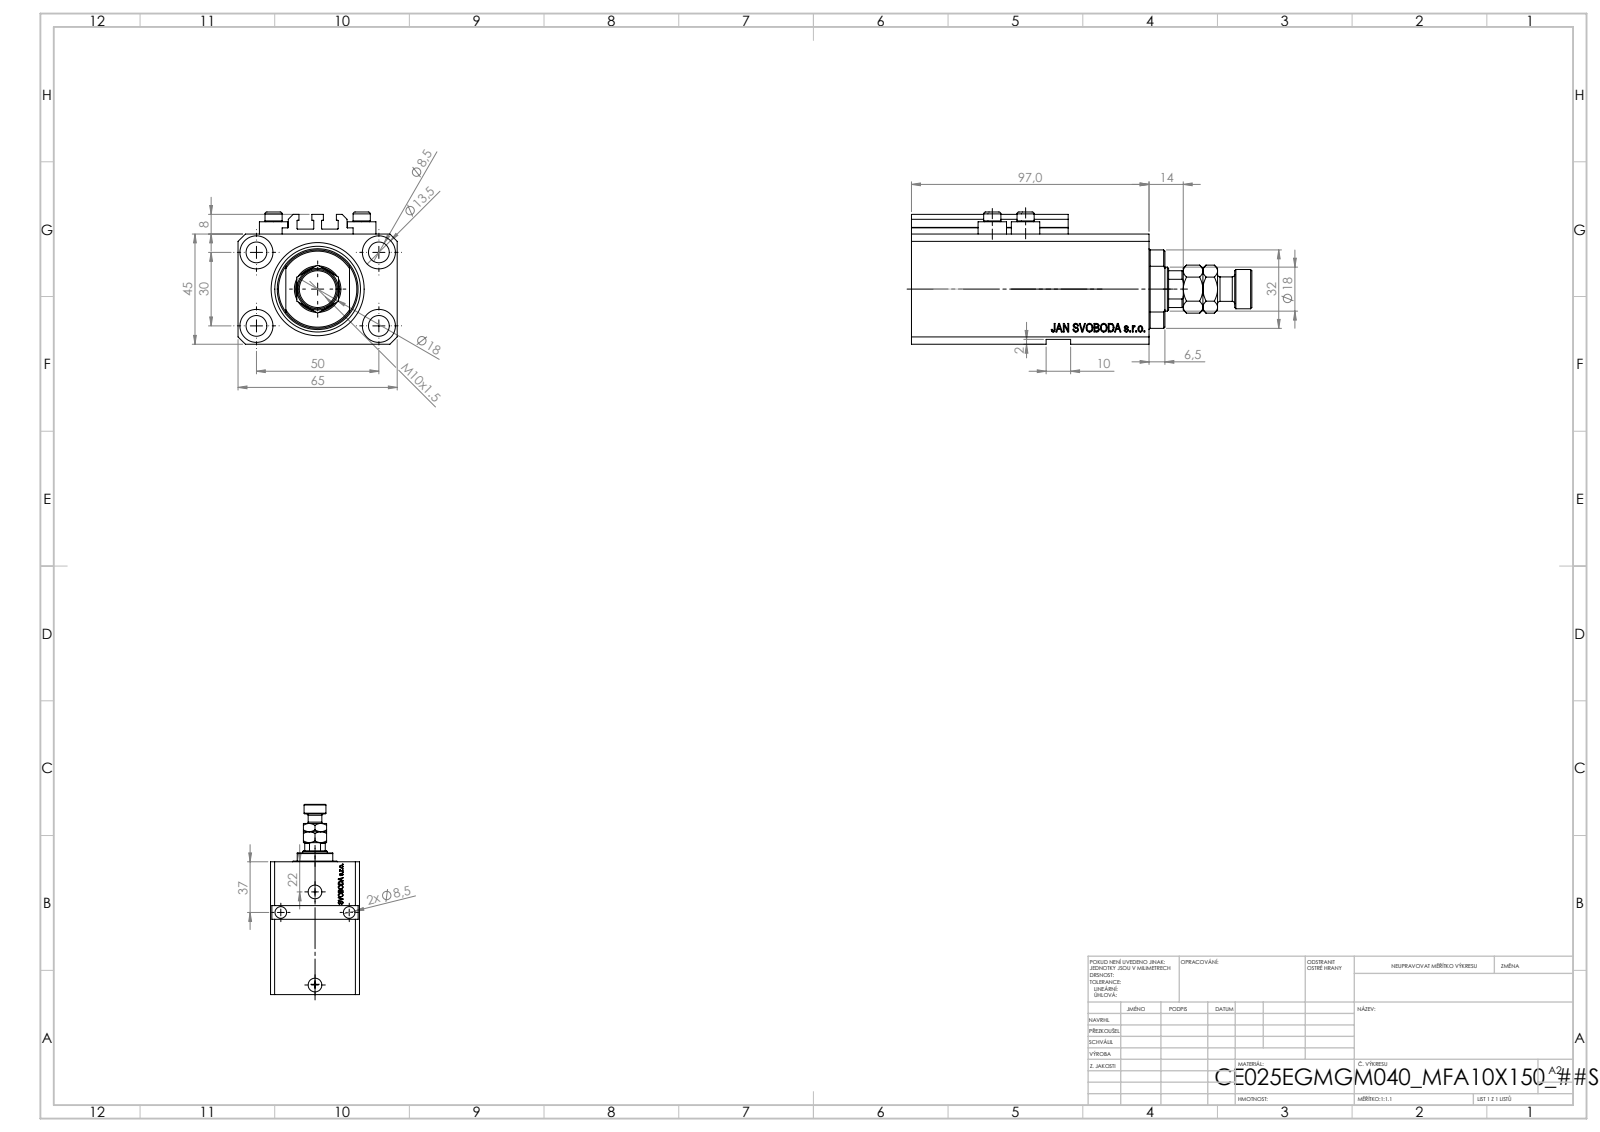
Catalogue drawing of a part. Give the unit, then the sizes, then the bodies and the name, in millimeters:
Units: millimetres
Overall size (bounding box): 139 × 50.5 × 43
Round holes (diameter × count): ⌀8.5 ×1, ⌀18 ×1
Round bosses / shafts (diameter × count): ⌀7 ×4, ⌀4 ×4, ⌀38 ×1, ⌀25 ×1, ⌀16 ×1, ⌀10 ×1
Partial cylindrical surfaces — rounded edges, fillets, slot ends (radius × count): R0.2 ×10, R8.5 ×1, R16 ×1
Main face-to-face distances: 6, 2, 20.5, 10, 2.5, 28, 8, 0.75, 6.05, 3.6
Volume: 62 945 mm³ · Surface area: 23 126 mm²
Bodies: 8 solids, 250 faces (102 planar, 46 cylindrical, 102 other)
Part name (STEP PRODUCT): V250CE_VC_E; ALLEN BOLT V250CE; V250CE_E_Body; MFA (+1 more)
STEP written by: SolidWorks 2019 (CONFIG_CONTROL_DESIGN)
